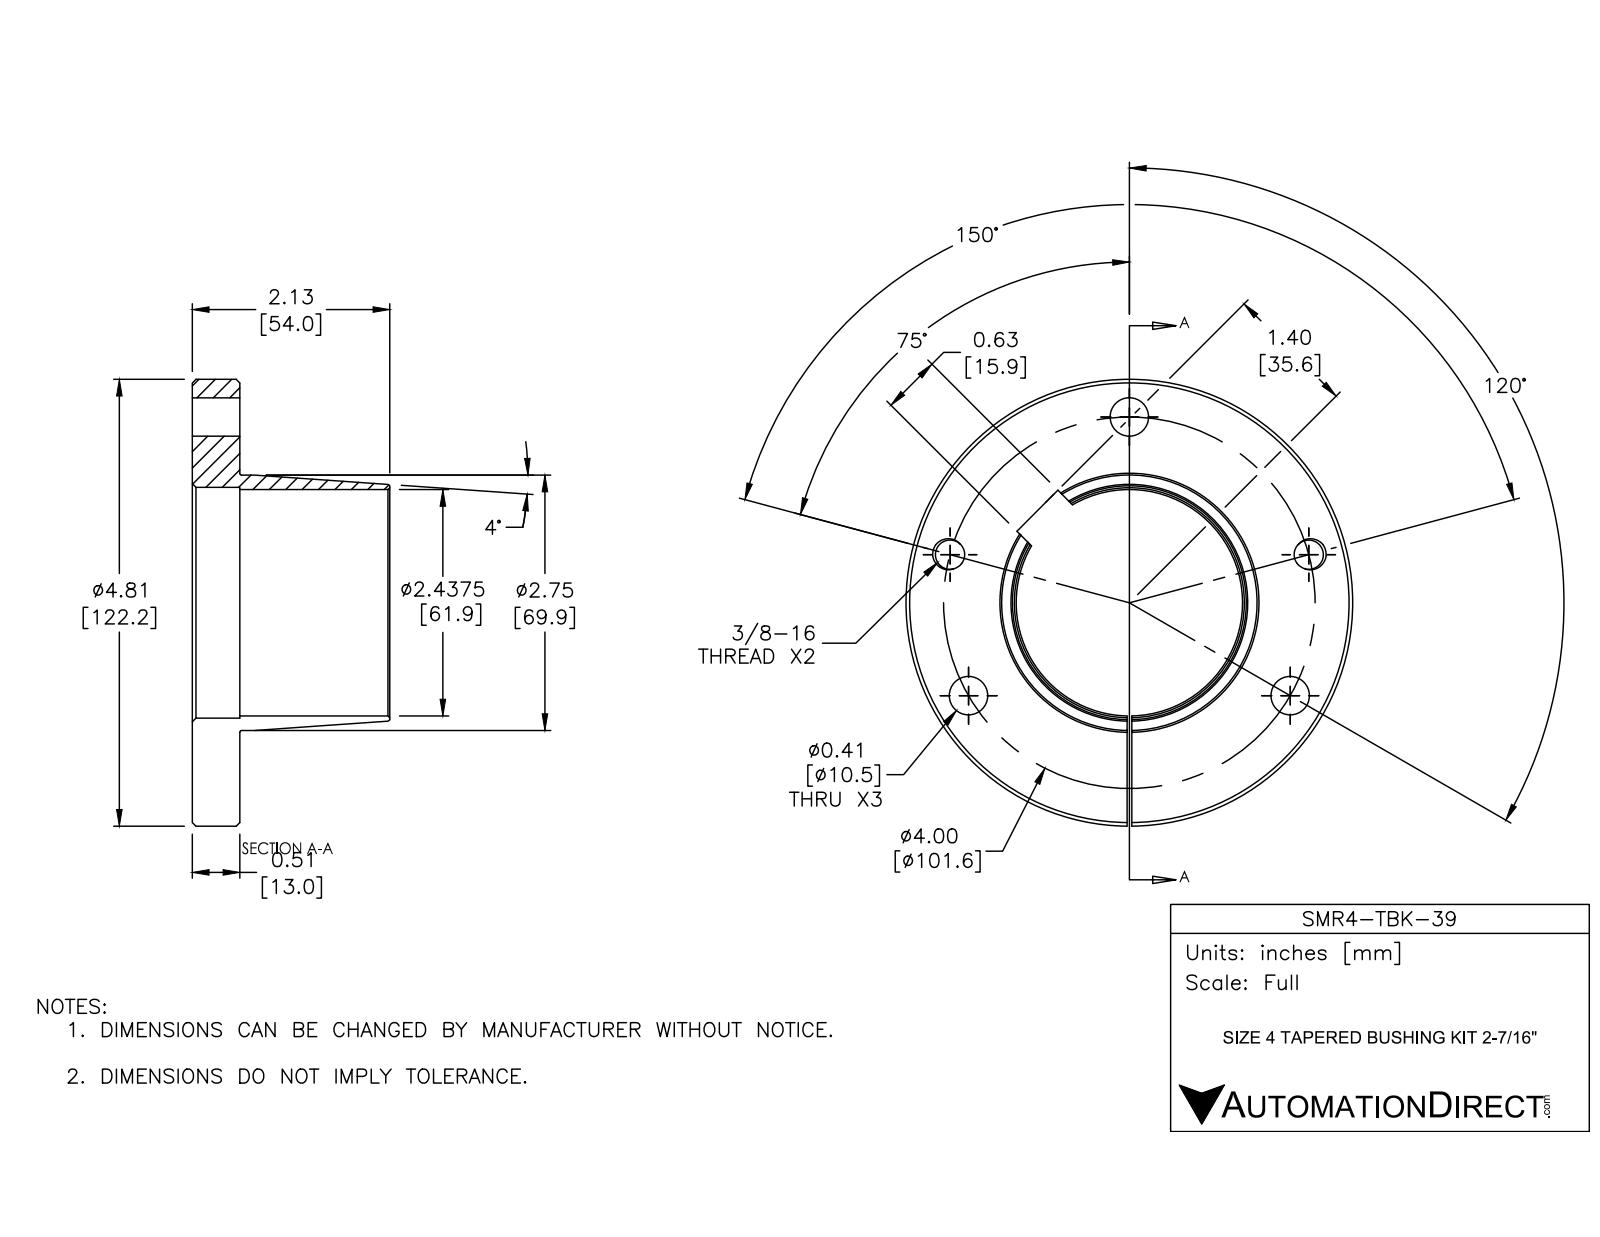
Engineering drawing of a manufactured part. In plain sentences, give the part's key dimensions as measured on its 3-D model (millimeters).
The part is named "SMR4-TBK-39". Its 3-D file was written by "SolidWorks 2016 (AUTOMOTIVE_DESIGN)". It is 1 solid with 127 faces: 11 planar, 92 cylindrical and 24 other. Overall it measures 122.2 by 122.2 by 54 millimeters. Its volume is 126 400 cubic millimeters and its surface area 41 810 square millimeters. Round holes: 3 of diameter 10.5, 2 of diameter 8, 2 of diameter 9.5, 1 of diameter 61.9, 1 of diameter 63.1. Round bosses or shafts: 1 of diameter 122.2, 1 of diameter 69.9. The main face-to-face distances are 13, 1.3, 15.9, 54, 41. The hole center spacings are 50.8, 38.9, 61.8, 88, 100.7, 88, 98.1.
